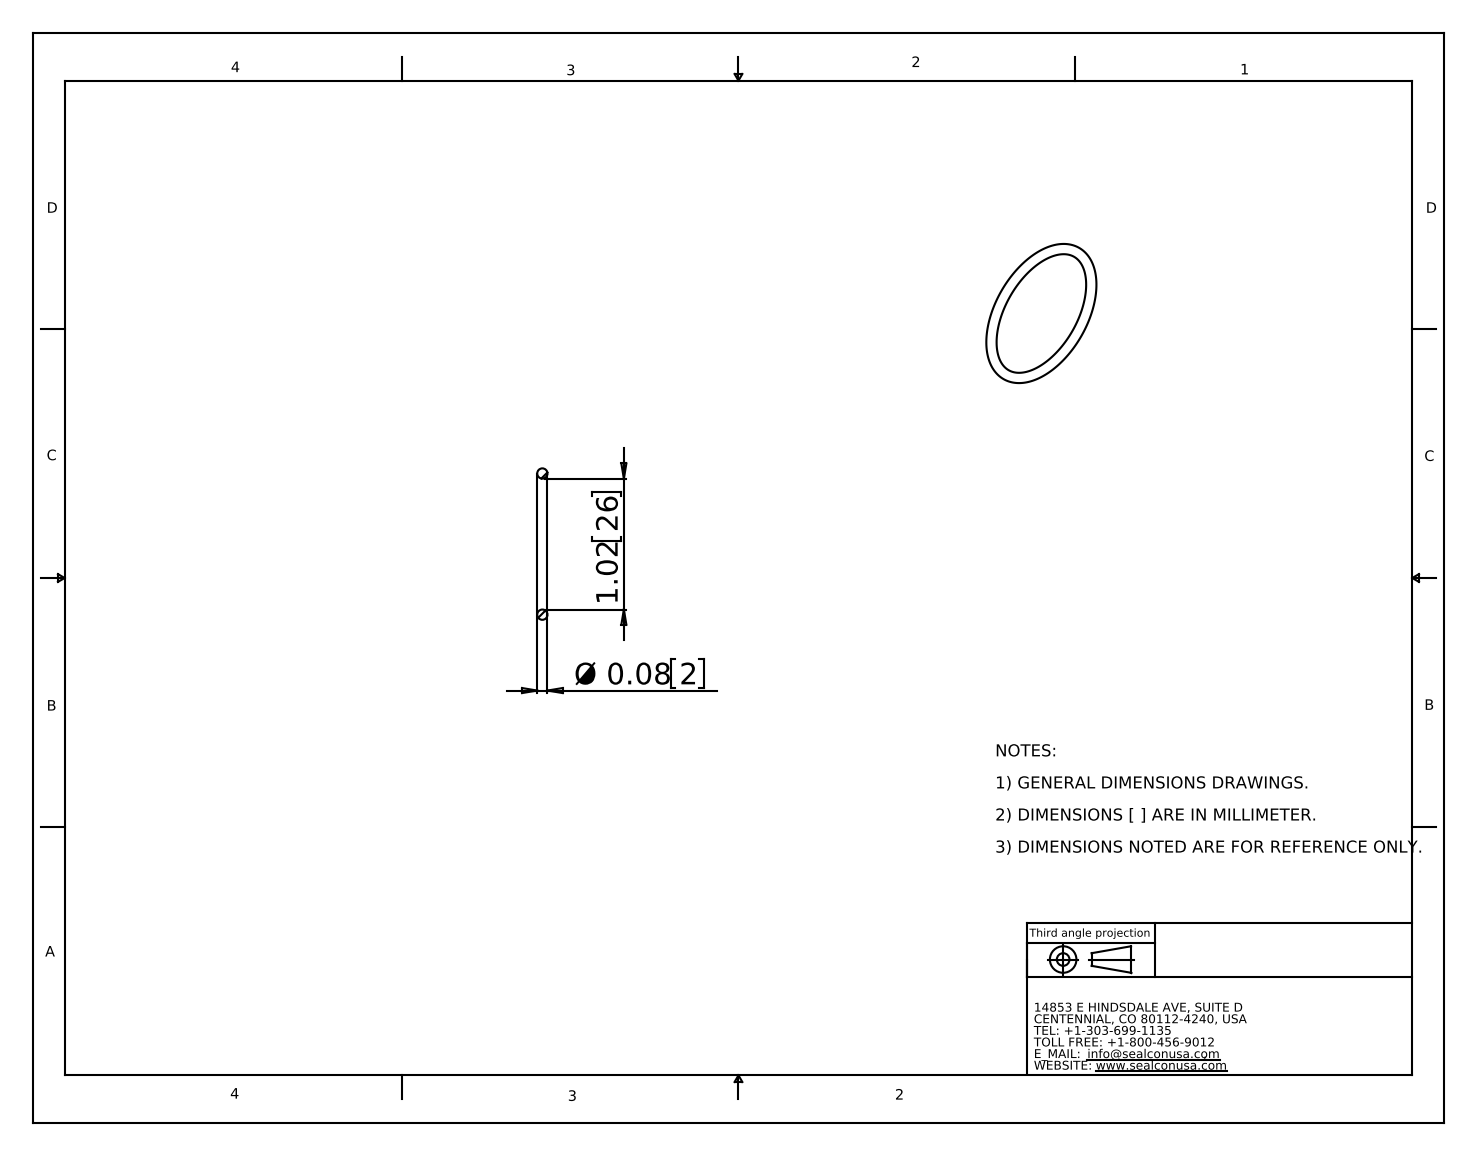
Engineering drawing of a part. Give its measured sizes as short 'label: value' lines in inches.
name: OR-21-SI
written by: SolidWorks 2008 (CONFIG_CONTROL_DESIGN)
unit: in
bodies: 1 solid, 4 faces (0 planar, 0 cylindrical, 4 other)
size: 1.18 × 1.18 × 0.08
volume: 0.017 in³; area: 0.869 in²
